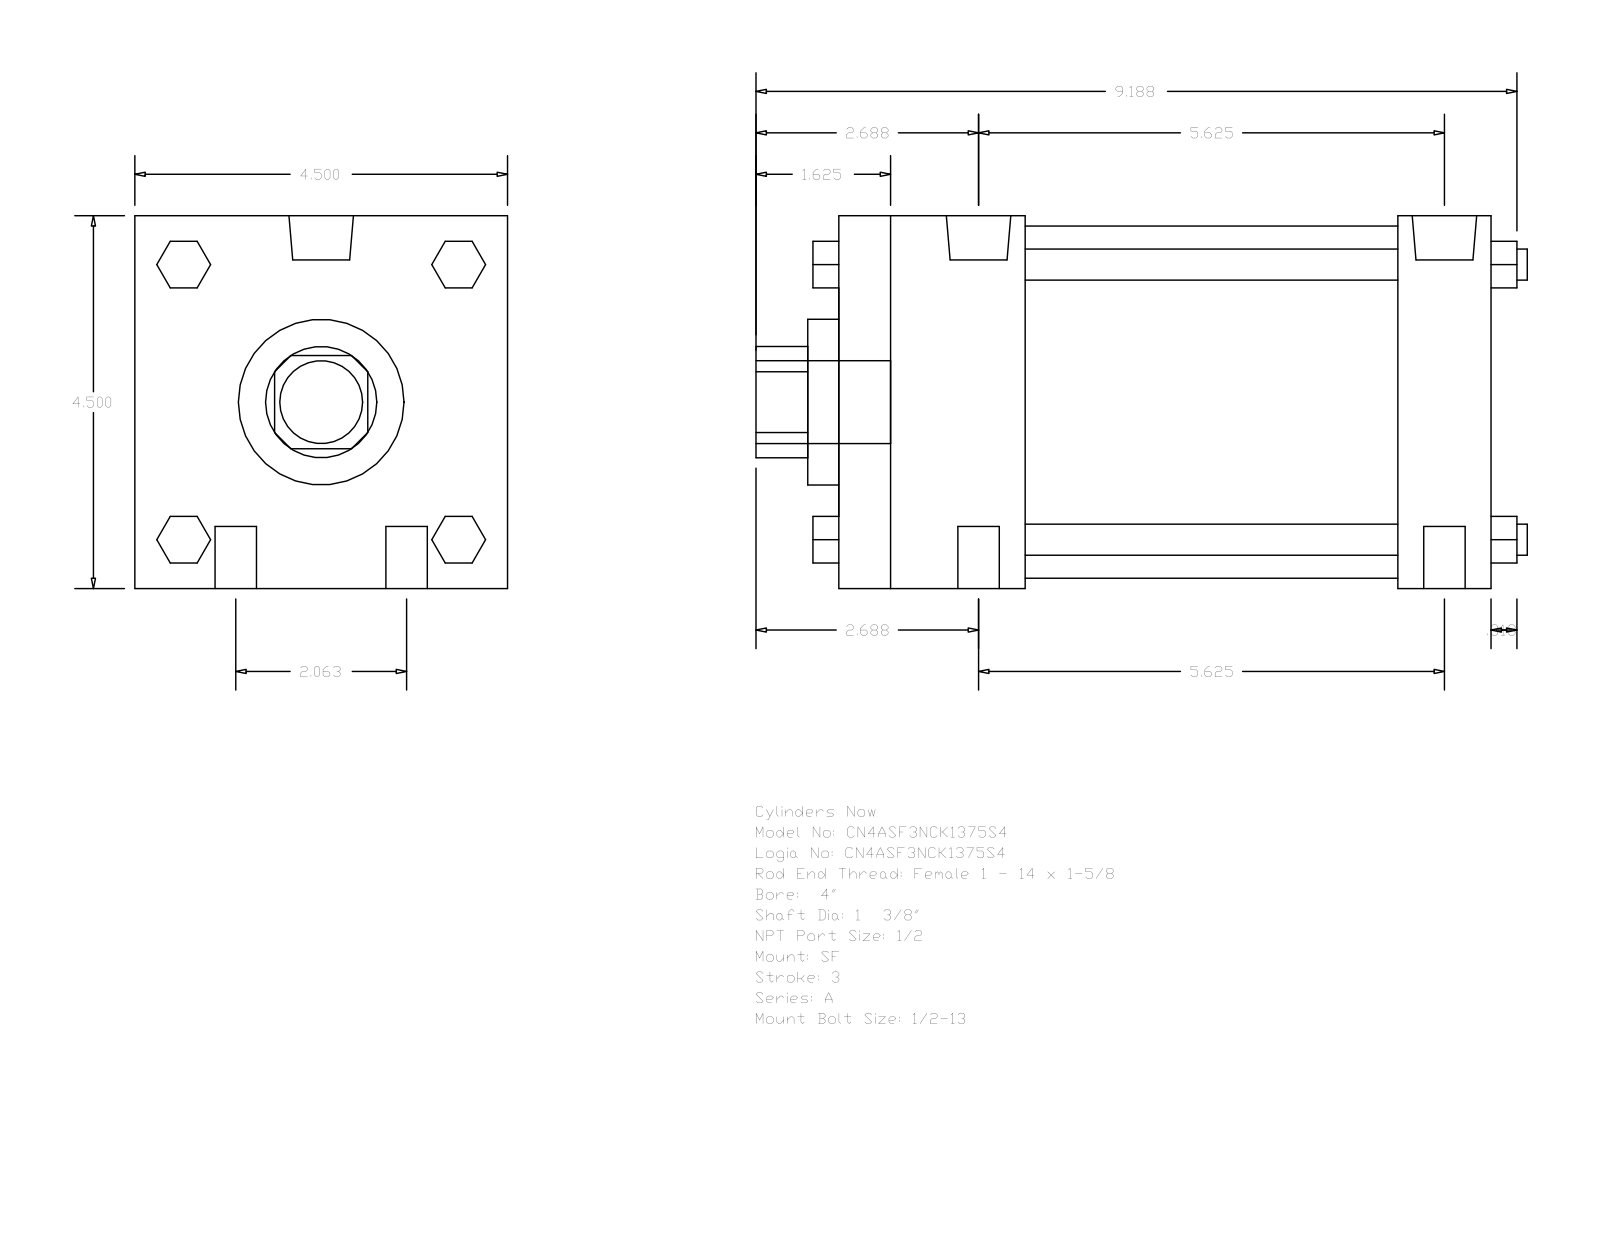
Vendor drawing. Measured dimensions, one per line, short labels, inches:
name: A_SF__0400_1.375
written by: GSSL Pune (CONFIG_CONTROL_DESIGN)
unit: in
bodies: 0 solids, 124 faces (94 planar, 30 cylindrical, 0 other)
size: 9.313 × 4.5 × 4.5
holes: 1× ⌀1.375, 1× ⌀2, 1× ⌀4.25
bosses: 4× ⌀0.5, 4× ⌀0.375, 2× ⌀0.778, 2× ⌀0.344, 1× ⌀1
rounds: 1× R0.672
face distances: 4.5, 7.875, 1.125, 6.75, 2.25, 5.625, 0.563, 0.375, 2.625, 7.125
